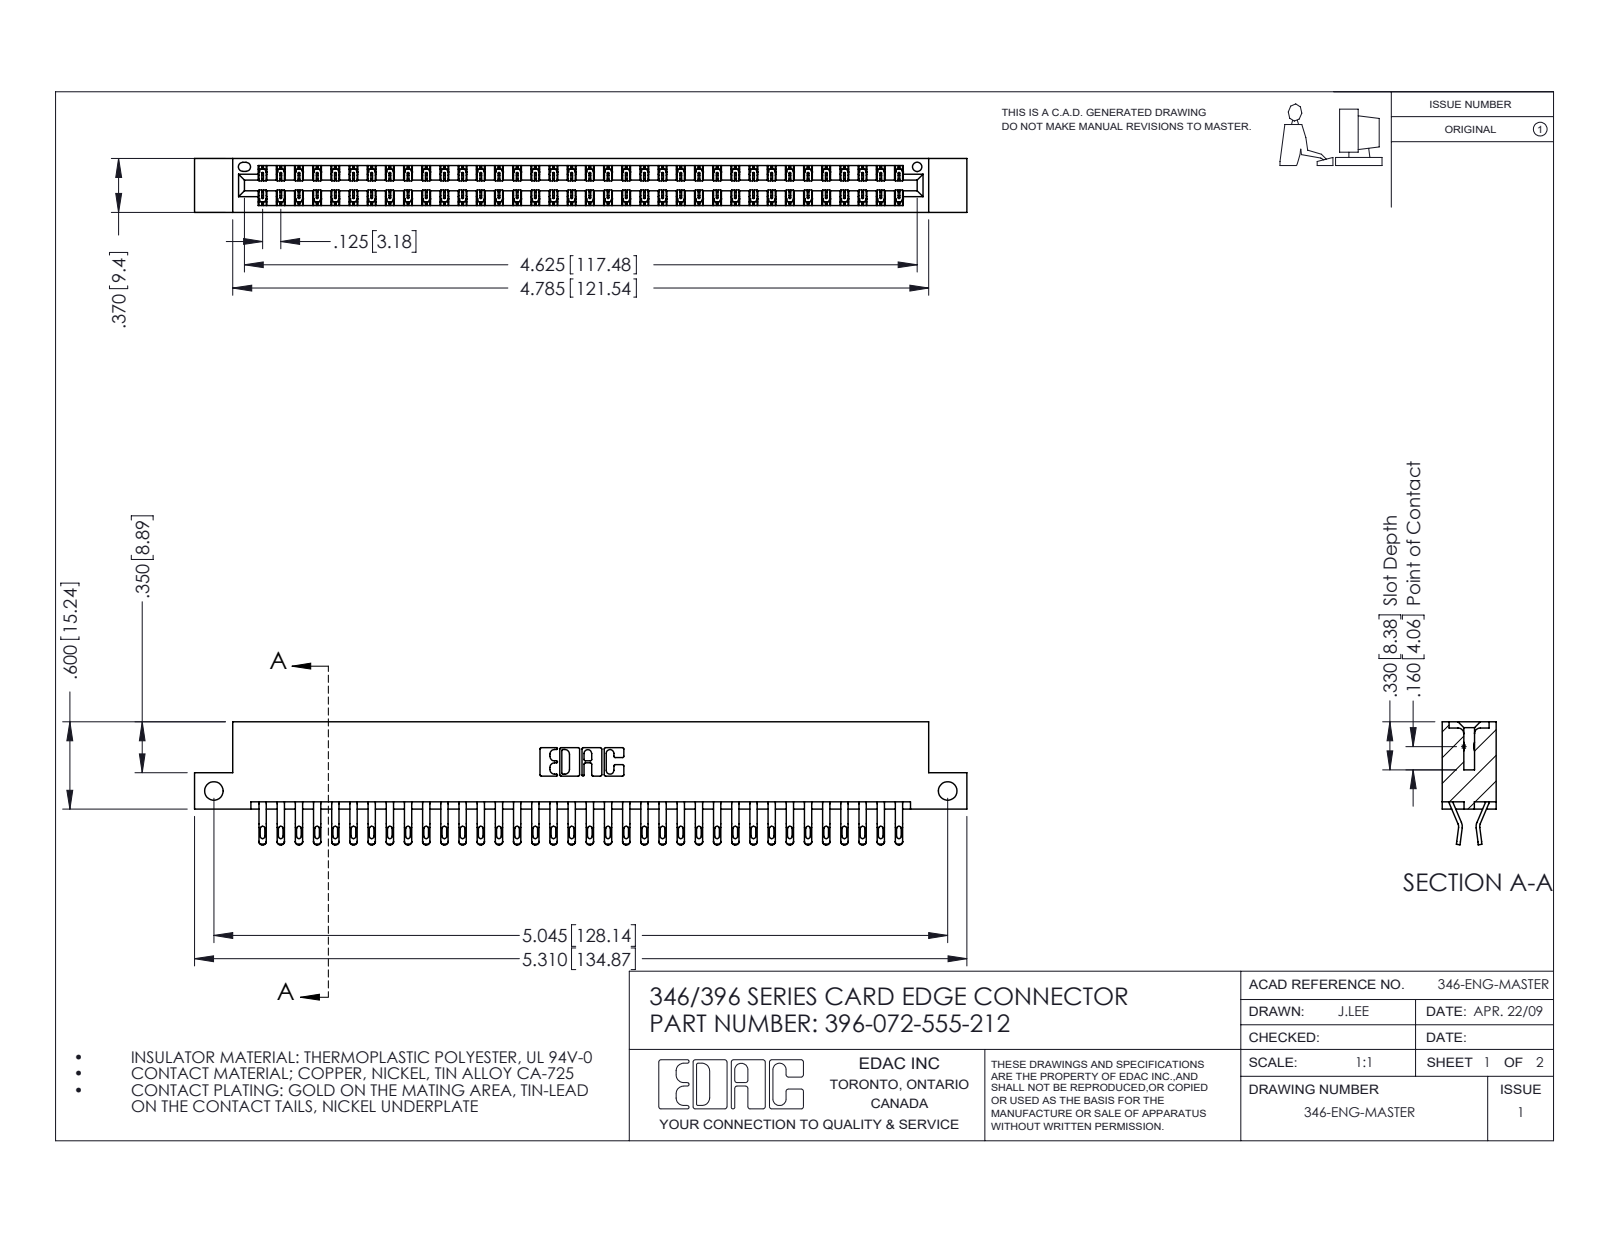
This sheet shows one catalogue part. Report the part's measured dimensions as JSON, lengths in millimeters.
{"part_name": "345-292-001_555 Tail; 396-072-555-212; 346 Part_Flush Mounting Lugs - Side Mount", "step_written_by": "SolidWorks 2016 (CONFIG_CONTROL_DESIGN)", "units": "millimeters", "bodies": {"solids": 73, "faces": 4298, "planar": 2452, "cylindrical": 1846, "other": 0}, "overall_size": [134.9, 21.5, 9.4], "volume_mm3": 13200, "surface_area_mm2": 18700, "round_holes": [[3.3, 2], [1.6, 1]], "partial_cylinders_radius": [[0.4, 144], [0.5, 144], [0.2, 108], [0.3, 22], [0.2, 6], [0.8, 6], [0.7, 3], [0.3, 2]], "face_to_face_distances": [1.2, 8.2, 9.4, 6.4, 0.6, 1.8, 7.6, 7, 3.8, 5.6], "hole_center_spacings": [128.1]}
